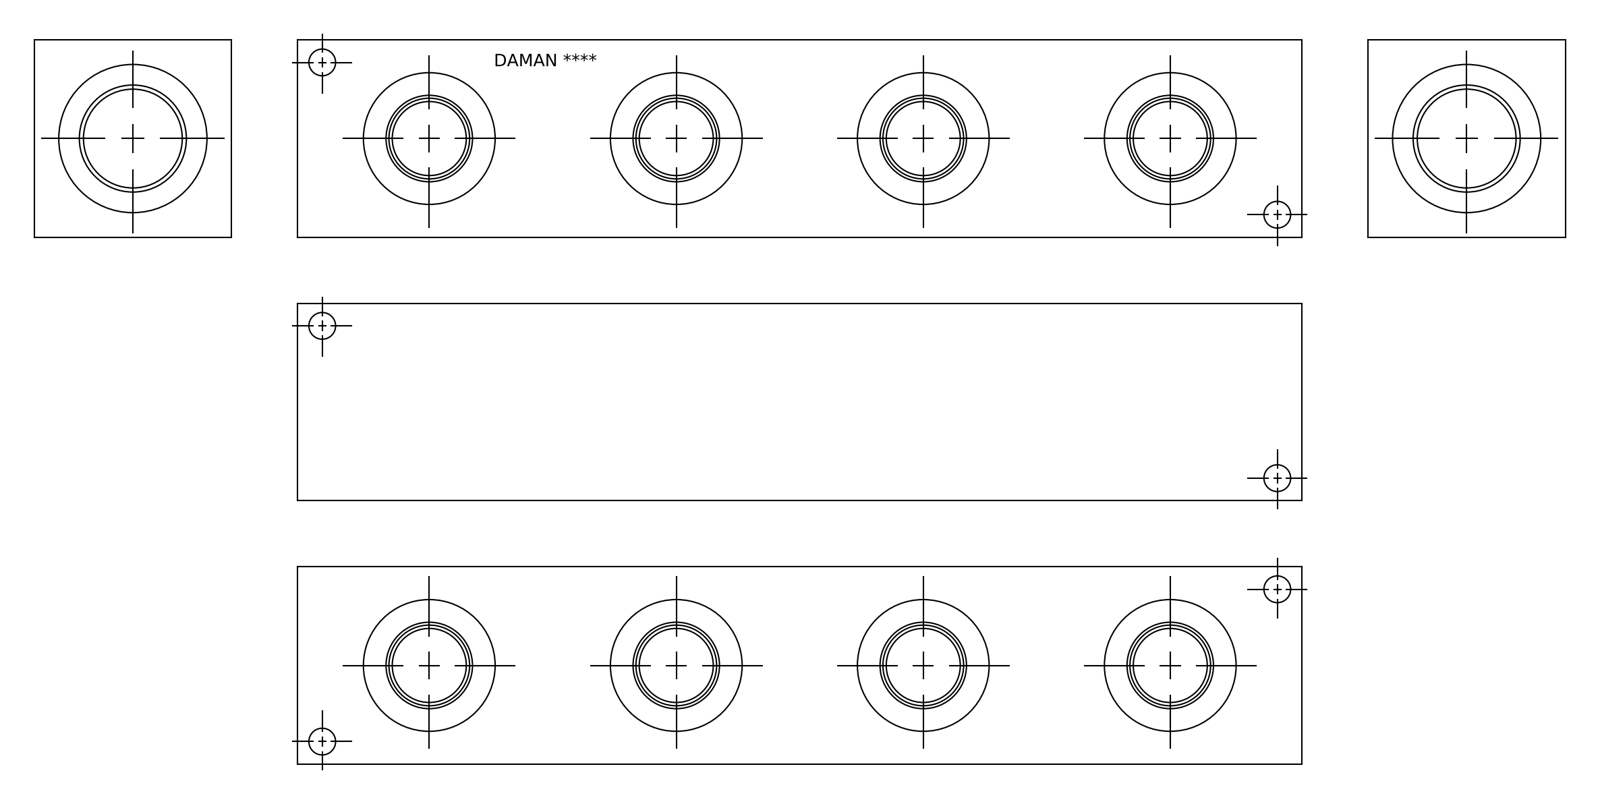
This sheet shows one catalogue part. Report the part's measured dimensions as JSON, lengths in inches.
{"part_name": "Part_+H1800416S_3D", "step_written_by": "Autodesk Inventor 2020 (AUTOMOTIVE_DESIGN)", "units": "inches", "bodies": {"solids": 1, "faces": 460, "planar": 249, "cylindrical": 65, "other": 146}, "overall_size": [15.25, 3, 3], "volume_in3": 115.6, "surface_area_in2": 263, "round_holes": [[0.406, 4], [1.125, 4], [1.231, 4], [1.313, 4], [1.329, 4], [1.398, 4], [1.934, 4], [1.313, 1], [1.5, 1], [1.544, 1], [1.625, 1], [1.625, 1]], "face_to_face_distances": [3, 0.031, 2.969, 2.938, 15.25, 15.219, 15.188, 0.781, 0.75, 2.219], "hole_center_spacings": [3.75, 1.994, 5.498, 7.5, 9.198, 12.927, 14.683, 11.25]}
